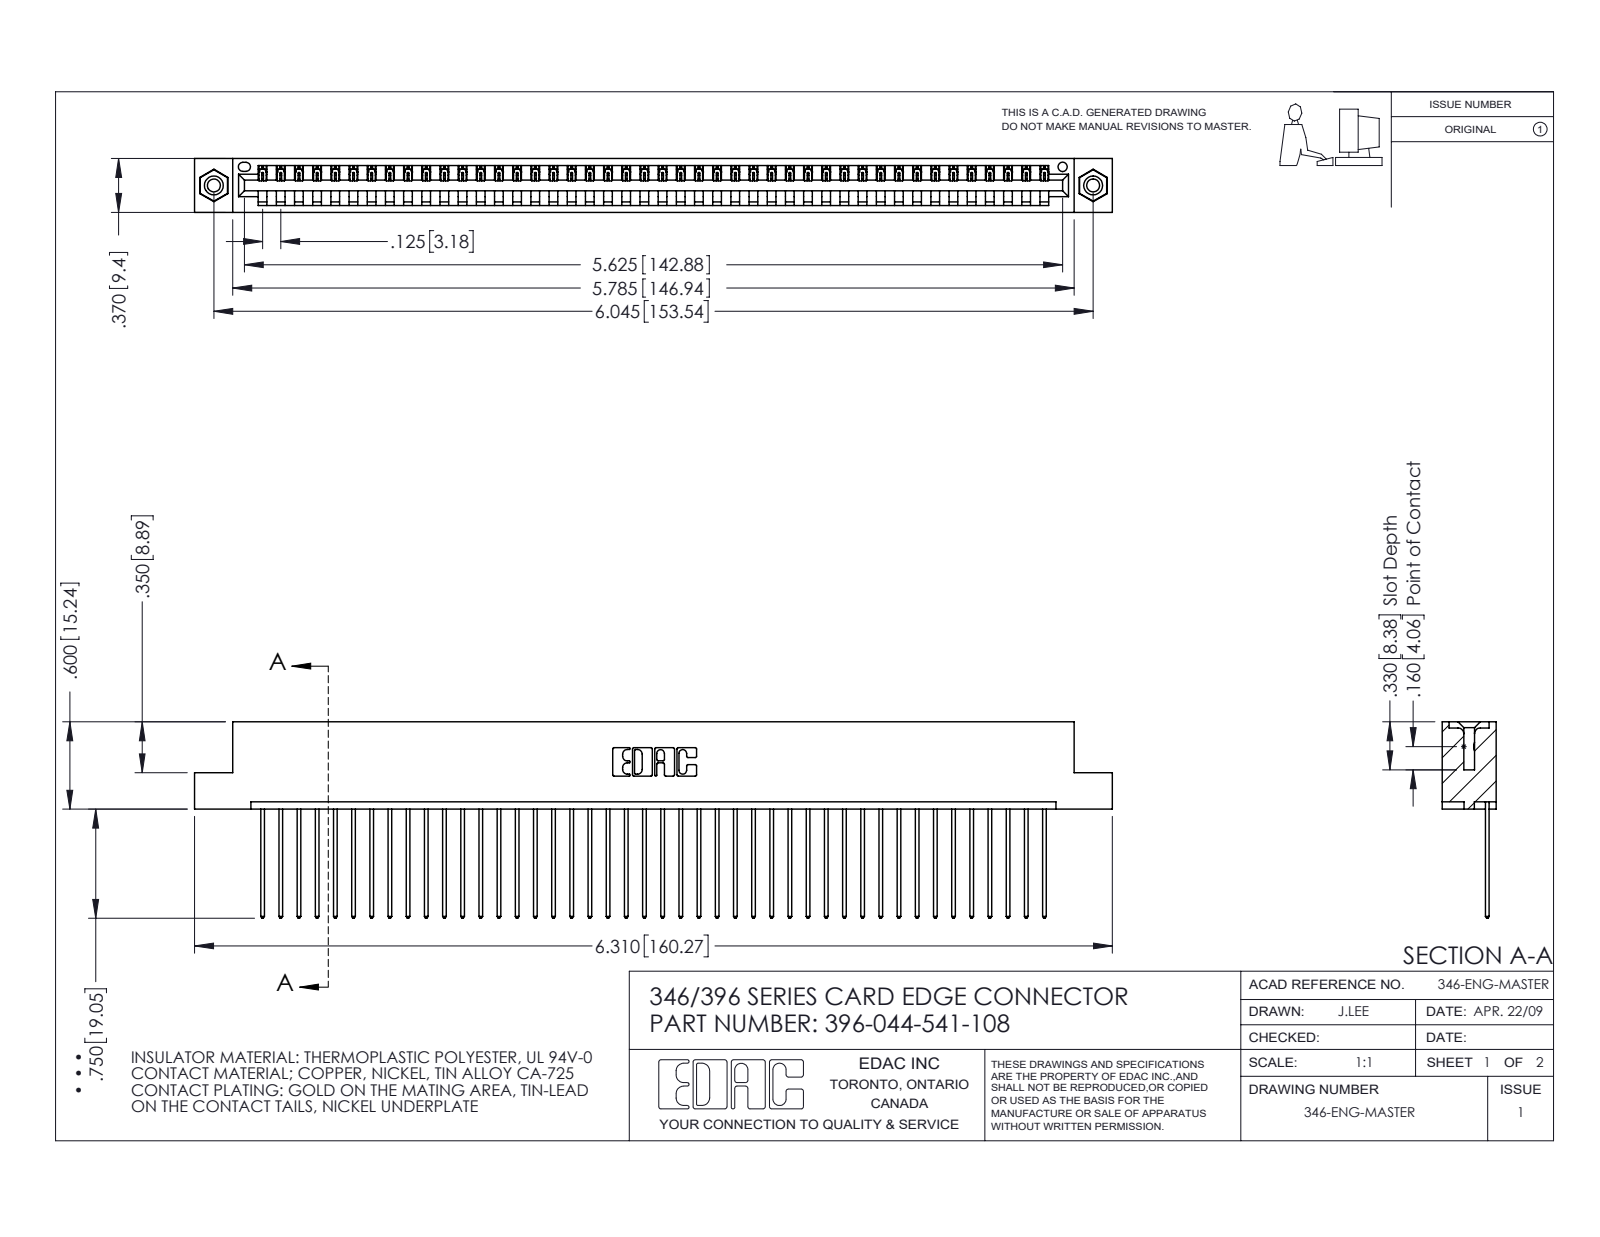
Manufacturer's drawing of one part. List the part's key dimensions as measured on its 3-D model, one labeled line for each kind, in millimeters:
Part name (STEP PRODUCT): 345-292-001_345-293-141; 345-250-001_345-250-003-102; 396-044-541-108; 346 Part_Flush Mounting Lugs - 0.156 Dia-TI
STEP written by: SolidWorks 2016 (CONFIG_CONTROL_DESIGN)
Units: millimetres
Bodies: 47 solids, 2734 faces (1868 planar, 850 cylindrical, 16 other)
Overall size (bounding box): 160.3 × 34.3 × 9.4
Volume: 15 500 mm³ · Surface area: 20 280 mm²
Round holes (diameter × count): ⌀2.3 ×2, ⌀3.2 ×2, ⌀4 ×2, ⌀1.6 ×1
Round bosses / shafts (diameter × count): ⌀3.9 ×2
Partial cylindrical surfaces — rounded edges, fillets, slot ends (radius × count): R0.2 ×88, R0.3 ×88, R0.3 ×22, R0.2 ×6, R0.8 ×6, R0.7 ×3, R0.8 ×2, R1 ×2
Main face-to-face distances: 1.2, 8.2, 9.4, 6.4, 1.8, 7.6, 0.6, 3.8, 5.6, 2.5
Hole centre spacings: 6.2, 148.2, 153.5
